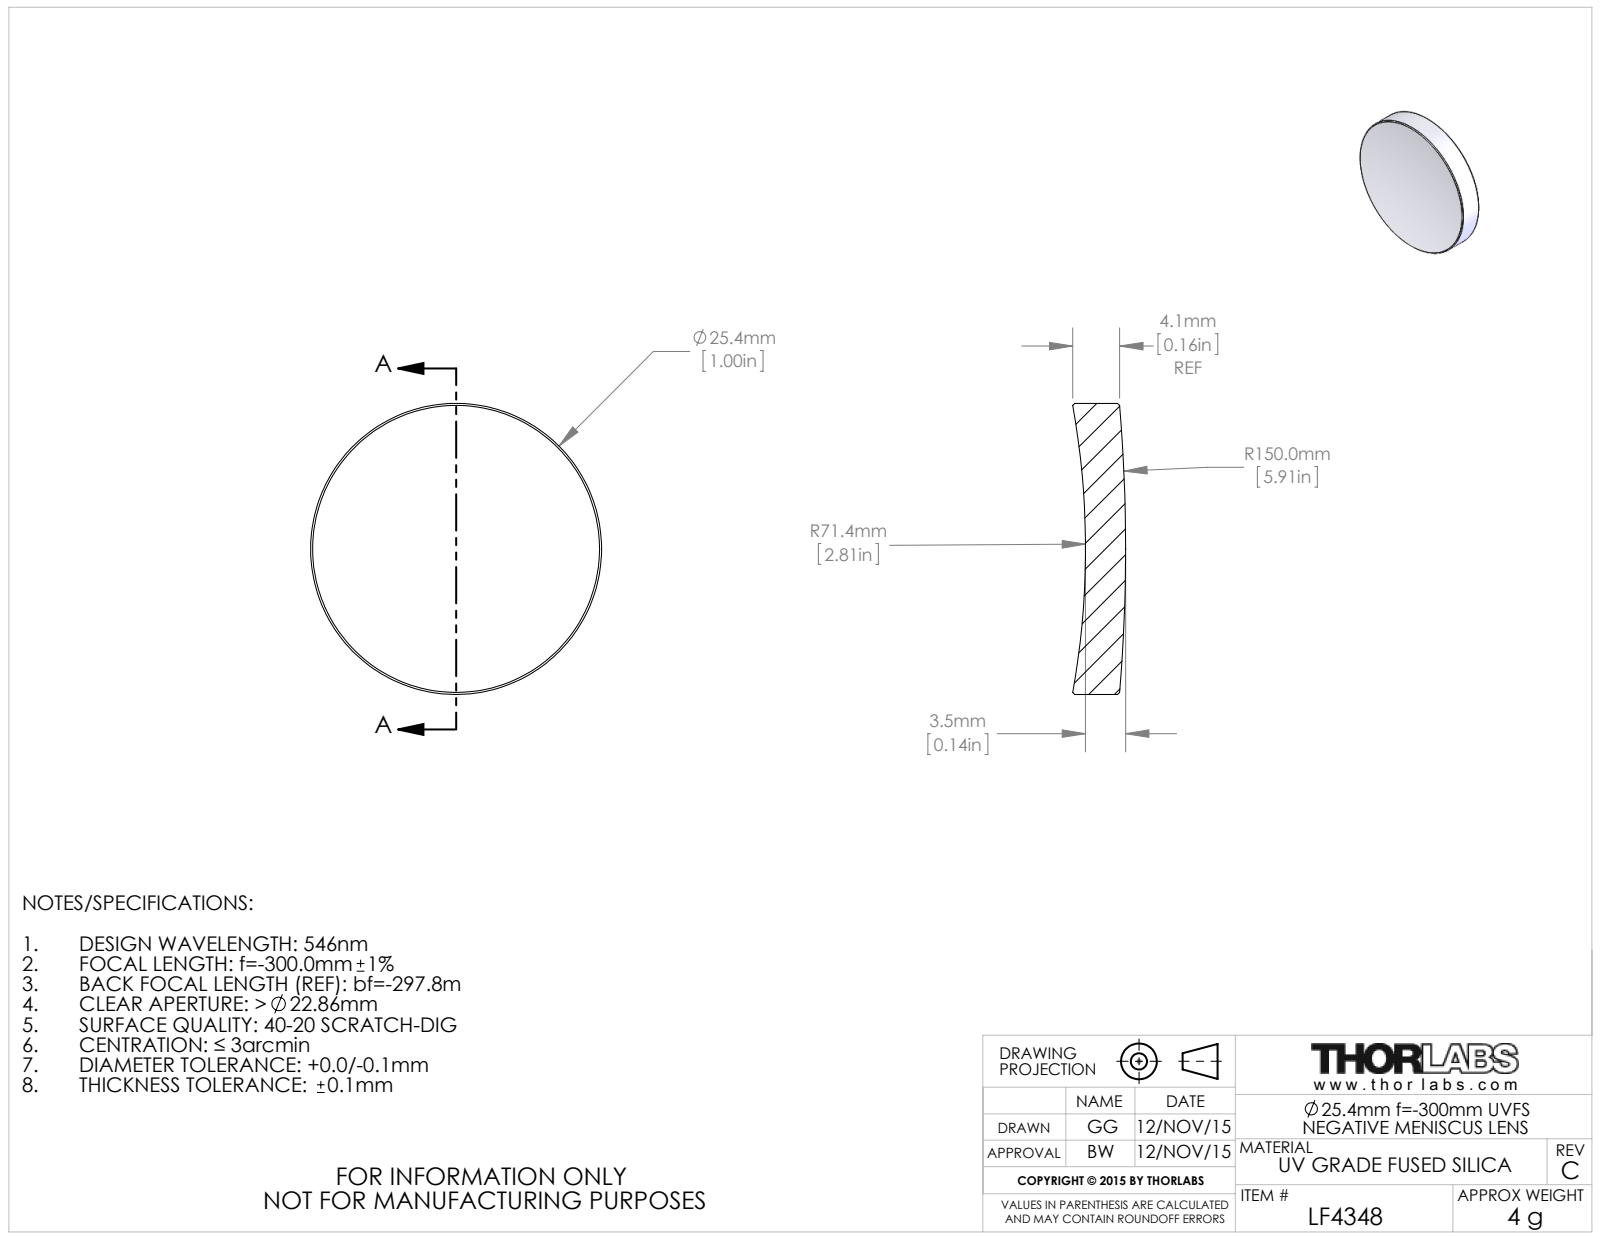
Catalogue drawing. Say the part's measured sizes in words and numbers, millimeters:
The part is named "4221-E0W". Its 3-D file was written by "SolidWorks 2014 (CONFIG_CONTROL_DESIGN)". It is 1 solid with 10 faces: 0 planar, 2 cylindrical and 8 other. Overall it measures 25.4 by 25.4 by 4.6 millimeters. Its volume is 1 920 cubic millimeters and its surface area 1 328 square millimeters. Round bosses or shafts: 1 of diameter 25.4.
